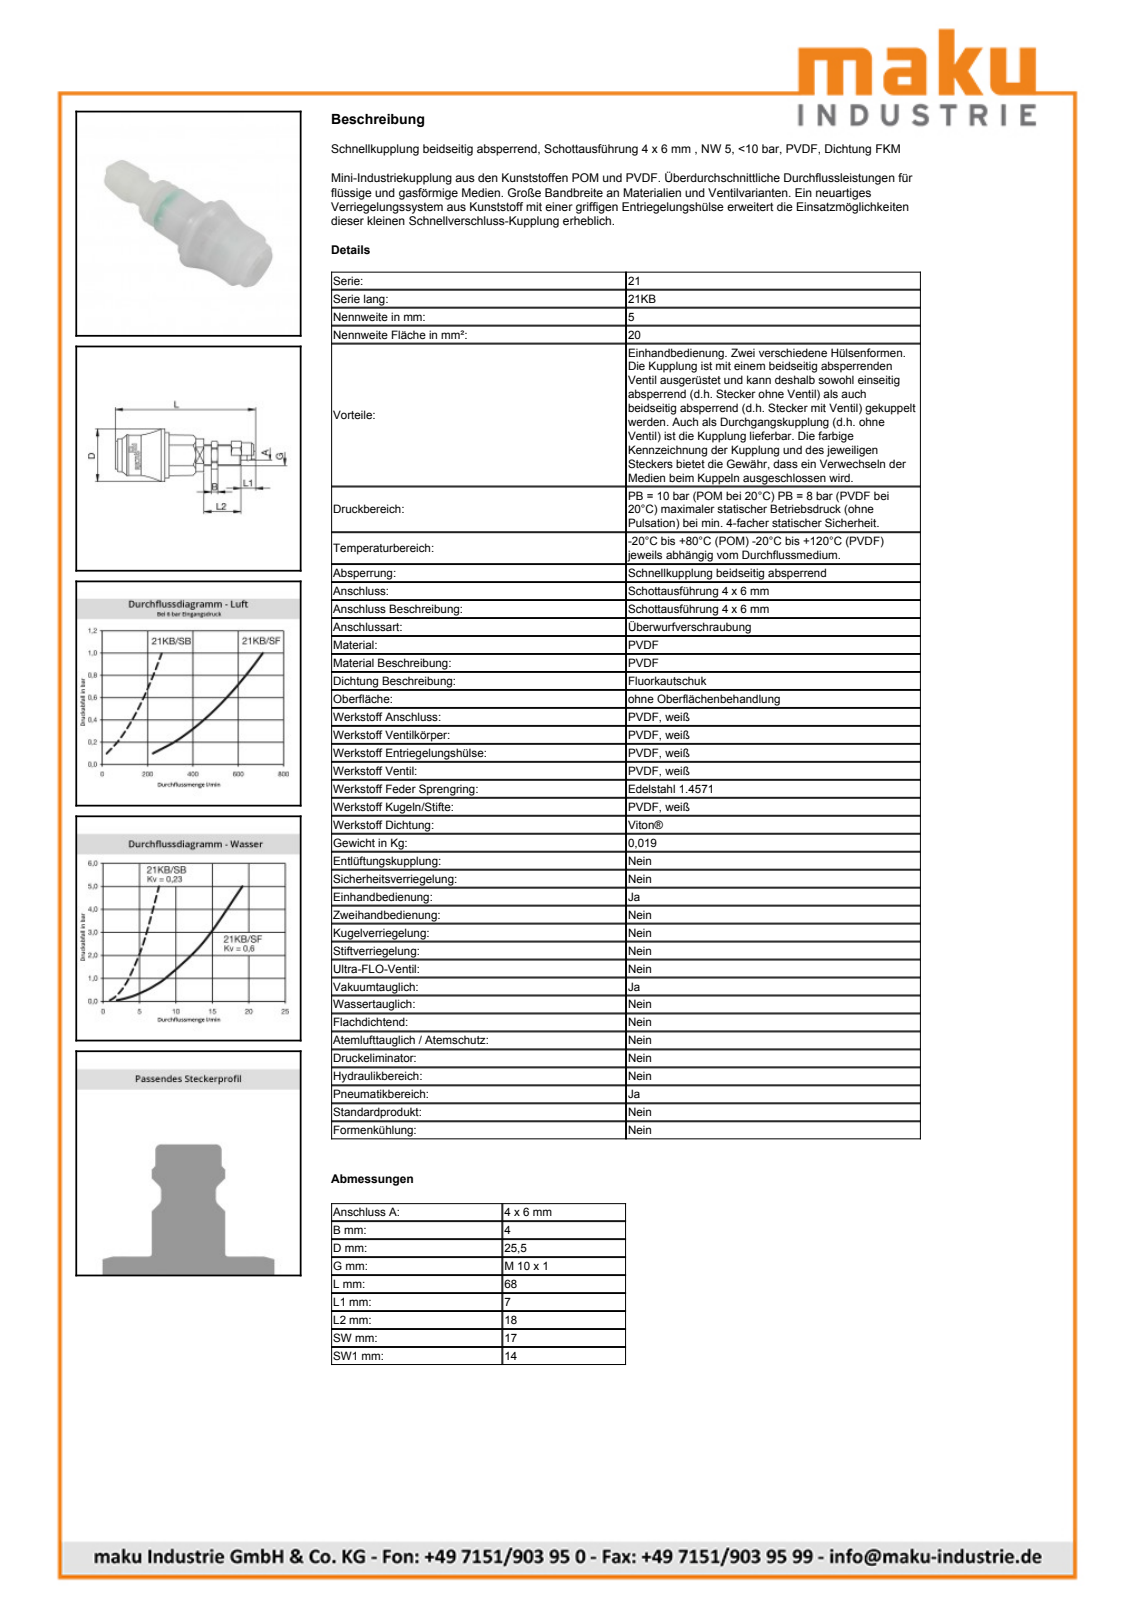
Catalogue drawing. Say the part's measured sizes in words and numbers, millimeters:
The part is named "D111168". Its 3-D file was written by "Autodesk Inventor 2013 (AUTOMOTIVE_DESIGN)". It is 2 solids with 483 faces: 184 planar, 83 cylindrical and 216 other. Overall it measures 54.15 by 16.15 by 16.15 millimeters. Its volume is 6 153 cubic millimeters and its surface area 6 316 square millimeters. Round holes: 1 of diameter 6.2, 1 of diameter 6.5, 1 of diameter 8.2, 1 of diameter 9, 1 of diameter 10.4, 1 of diameter 10.45, 1 of diameter 10.5, 1 of diameter 10.7, 1 of diameter 12.15, 1 of diameter 14. Round bosses or shafts: 1 of diameter 16.15, 1 of diameter 15.1, 1 of diameter 12, 1 of diameter 11.4, 1 of diameter 11.15, 1 of diameter 10, 1 of diameter 4.6, 1 of diameter 3.95. Partial cylindrical surfaces (rounded edges, fillets, slot ends): 1 of radius 6.7, 1 of radius 6.75, 1 of radius 7.45, 1 of radius 7.9. The main face-to-face distances are 14, 12, 25.9, 29.15, 6, 11, 27.15, 2, 47.05, 19.9.
